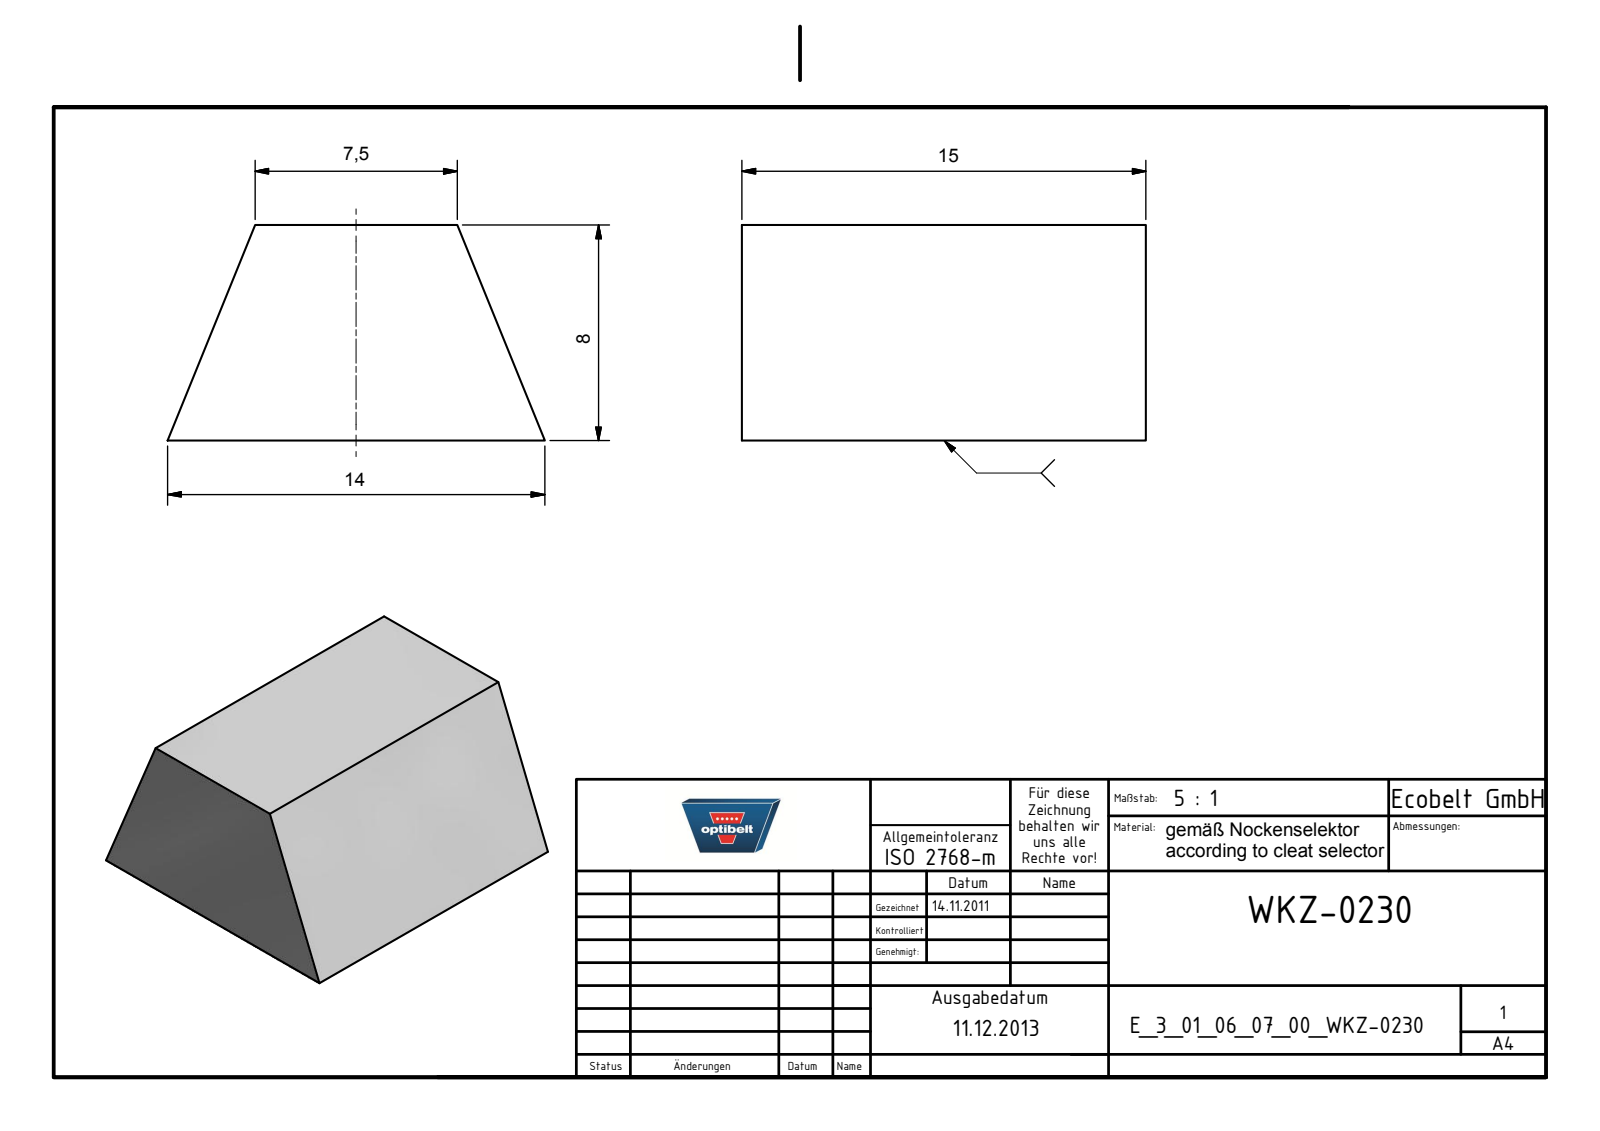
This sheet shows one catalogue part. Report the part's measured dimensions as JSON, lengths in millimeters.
{"part_name": "E_3_01_06_07_00_WKZ-0230", "step_written_by": "Autodesk Inventor 2025 (AUTOMOTIVE_DESIGN)", "units": "millimeters", "bodies": {"solids": 1, "faces": 6, "planar": 6, "cylindrical": 0, "other": 0}, "overall_size": [15, 14, 8], "volume_mm3": 1290, "surface_area_mm2": 754, "face_to_face_distances": [8, 15]}
